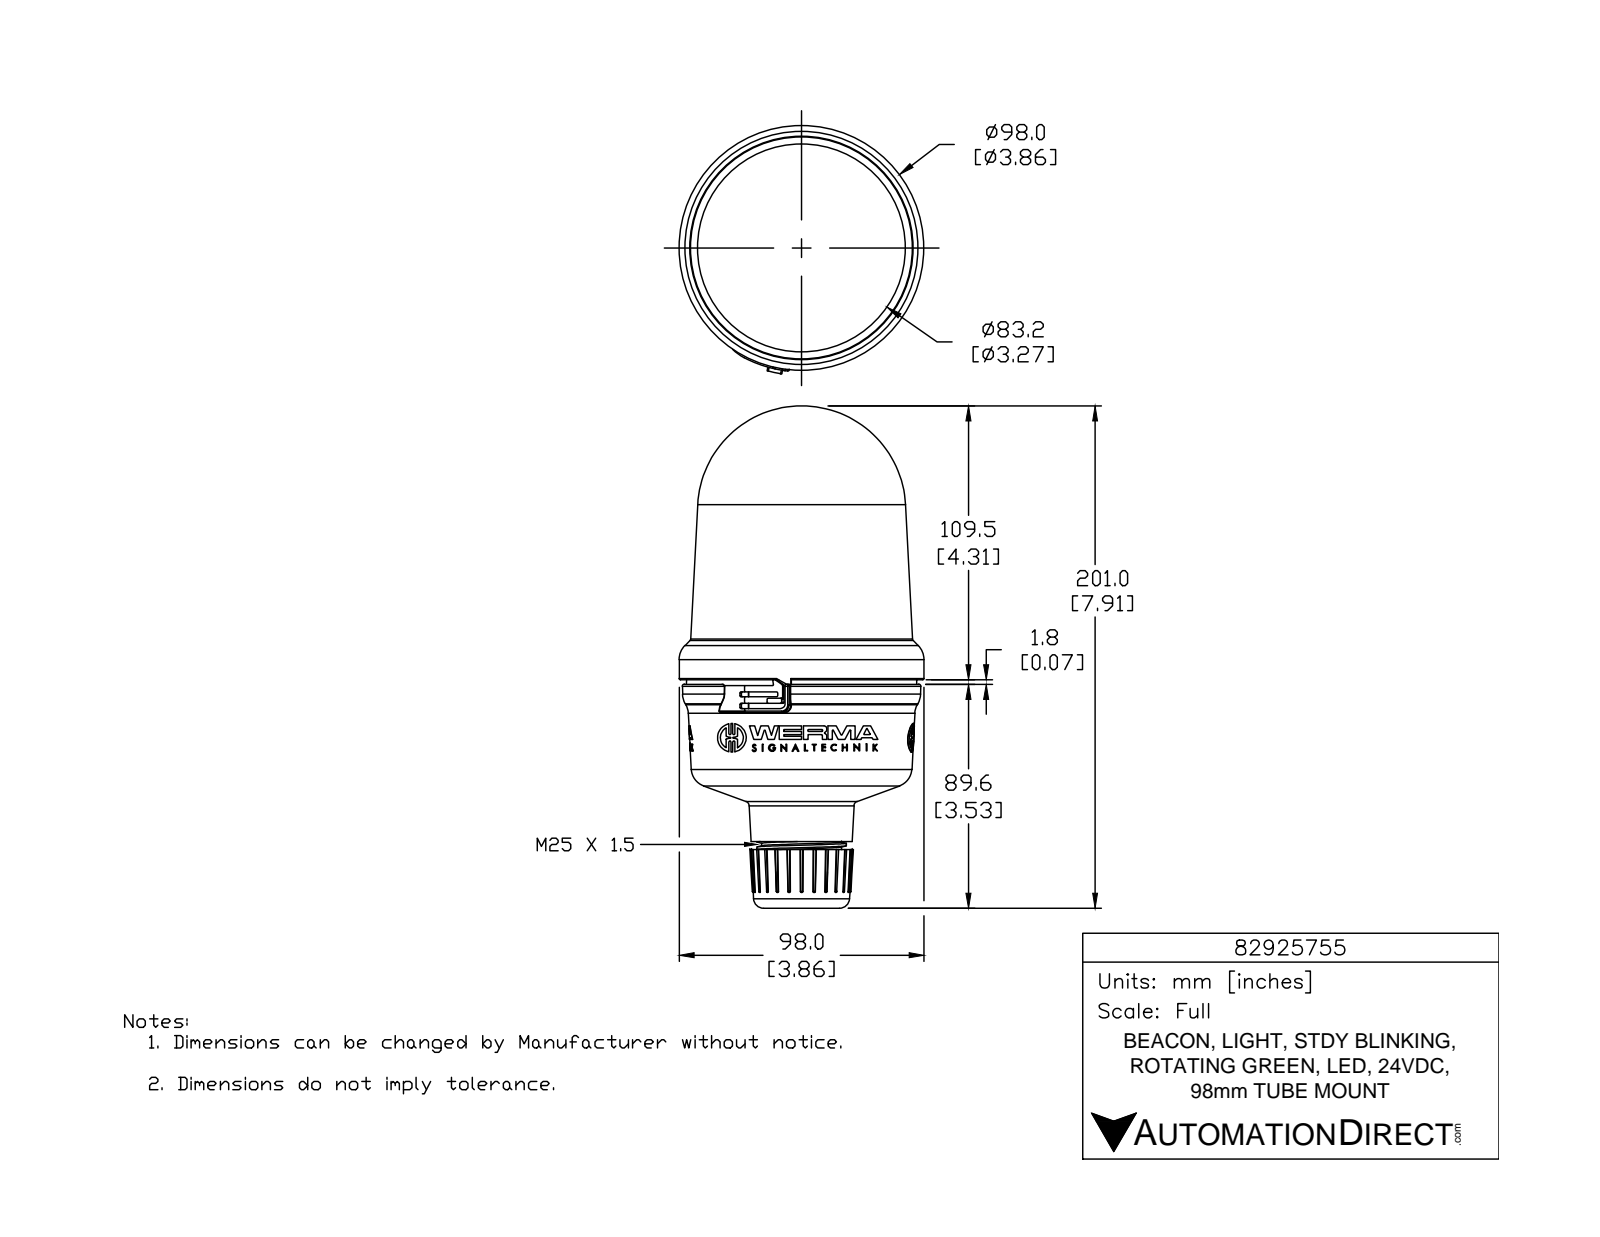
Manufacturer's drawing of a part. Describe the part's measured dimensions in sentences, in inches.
The part is named "82925755". Its 3-D file was written by "SolidWorks 2015 (AUTOMOTIVE_DESIGN)". It is 1 solid with 1006 faces: 554 planar, 189 cylindrical and 263 other. Overall it measures 7.914 by 3.912 by 3.858 inches. Its volume is 54.7 cubic inches and its surface area 91.39 square inches. Round holes: 3 of diameter 0.078, 1 of diameter 1.013, 1 of diameter 1.024. Round bosses or shafts: 3 of diameter 0.452, 3 of diameter 0.113, 1 of diameter 3.858, 1 of diameter 1.409, 1 of diameter 1.261. Partial cylindrical surfaces (rounded edges, fillets, slot ends): 12 of radius 0.02, 9 of radius 0.007, 6 of radius 0.007, 6 of radius 0.016, 6 of radius 0.016, 6 of radius 0.016, 6 of radius 0.262, 3 of radius 0.006. The main face-to-face distances are 2.214, 0.462, 2.676, 0.335, 0.127, 2.548, 2.603, 2.476, 2.141, 0.073.
